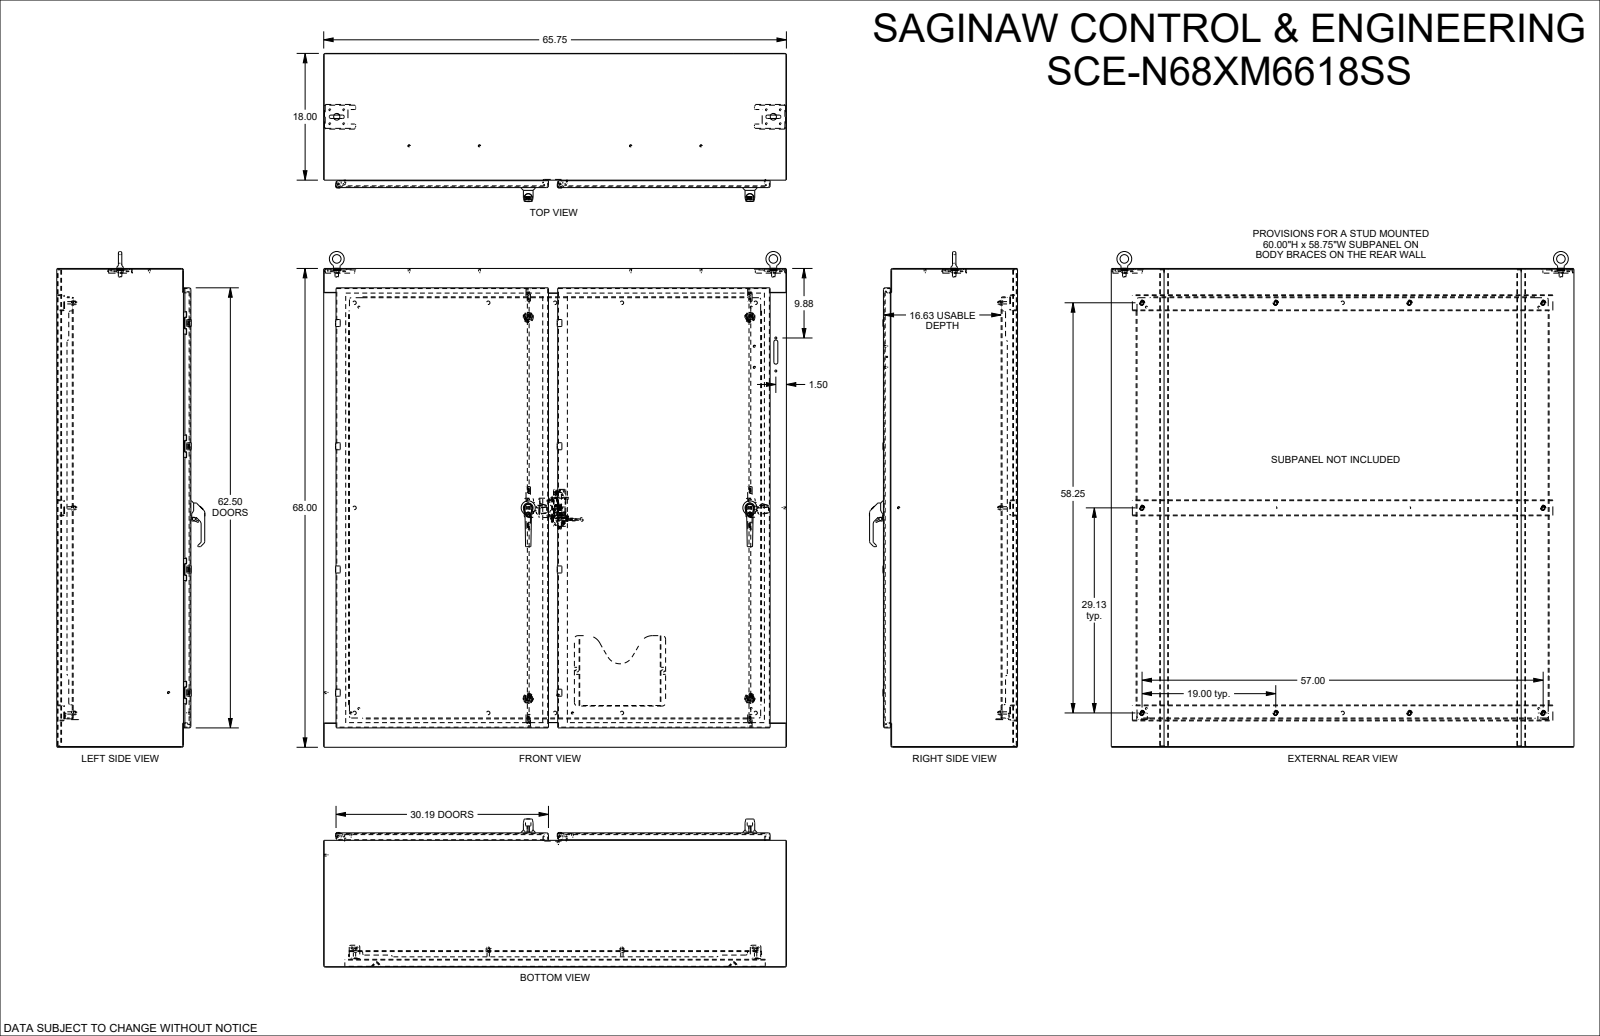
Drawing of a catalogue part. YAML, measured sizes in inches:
part_name: "SCE-N68XM6618"
step_written_by: "SolidWorks 2023 (AUTOMOTIVE_DESIGN)"
units: inches
bodies: {solids: 47, faces: 7355, planar: 3051, cylindrical: 2464, other: 1840}
overall_size: [70.945, 65.75, 21.046]
volume: 1744
surface_area: 33148
round_holes:
  - {diameter: 0.205, count: 16}
  - {diameter: 0.244, count: 16}
  - {diameter: 0.25, count: 14}
  - {diameter: 0.04, count: 8}
  - {diameter: 0.17, count: 8}
  - {diameter: 0.218, count: 8}
  - {diameter: 0.375, count: 8}
  - {diameter: 0.375, count: 8}
  - {diameter: 0.115, count: 4}
  - {diameter: 0.2, count: 4}
  - {diameter: 0.256, count: 4}
  - {diameter: 0.343, count: 4}
round_bosses_or_shafts:
  - {diameter: 0.17, count: 24}
  - {diameter: 0.25, count: 19}
  - {diameter: 0.24, count: 16}
  - {diameter: 0.196, count: 10}
  - {diameter: 1.4, count: 4}
  - {diameter: 0.341, count: 4}
  - {diameter: 2.008, count: 2}
  - {diameter: 1.173, count: 2}
partial_cylinders:
  - {radius: 0.03, count: 211}
  - {radius: 0.015, count: 162}
  - {radius: 0.125, count: 64}
  - {radius: 0.02, count: 63}
  - {radius: 0.04, count: 59}
  - {radius: 0.062, count: 52}
  - {radius: 0.02, count: 48}
  - {radius: 0.039, count: 42}
face_to_face_distances: [0.104, 18.954, 18.85, 19.058, 17.896, 1.058, 65.646, 67.896, 17.792, 1.162]
hole_center_spacings: [17.5, 35, 31.5, 28.326, 0.984, 1.399, 1.4, 1.548]
